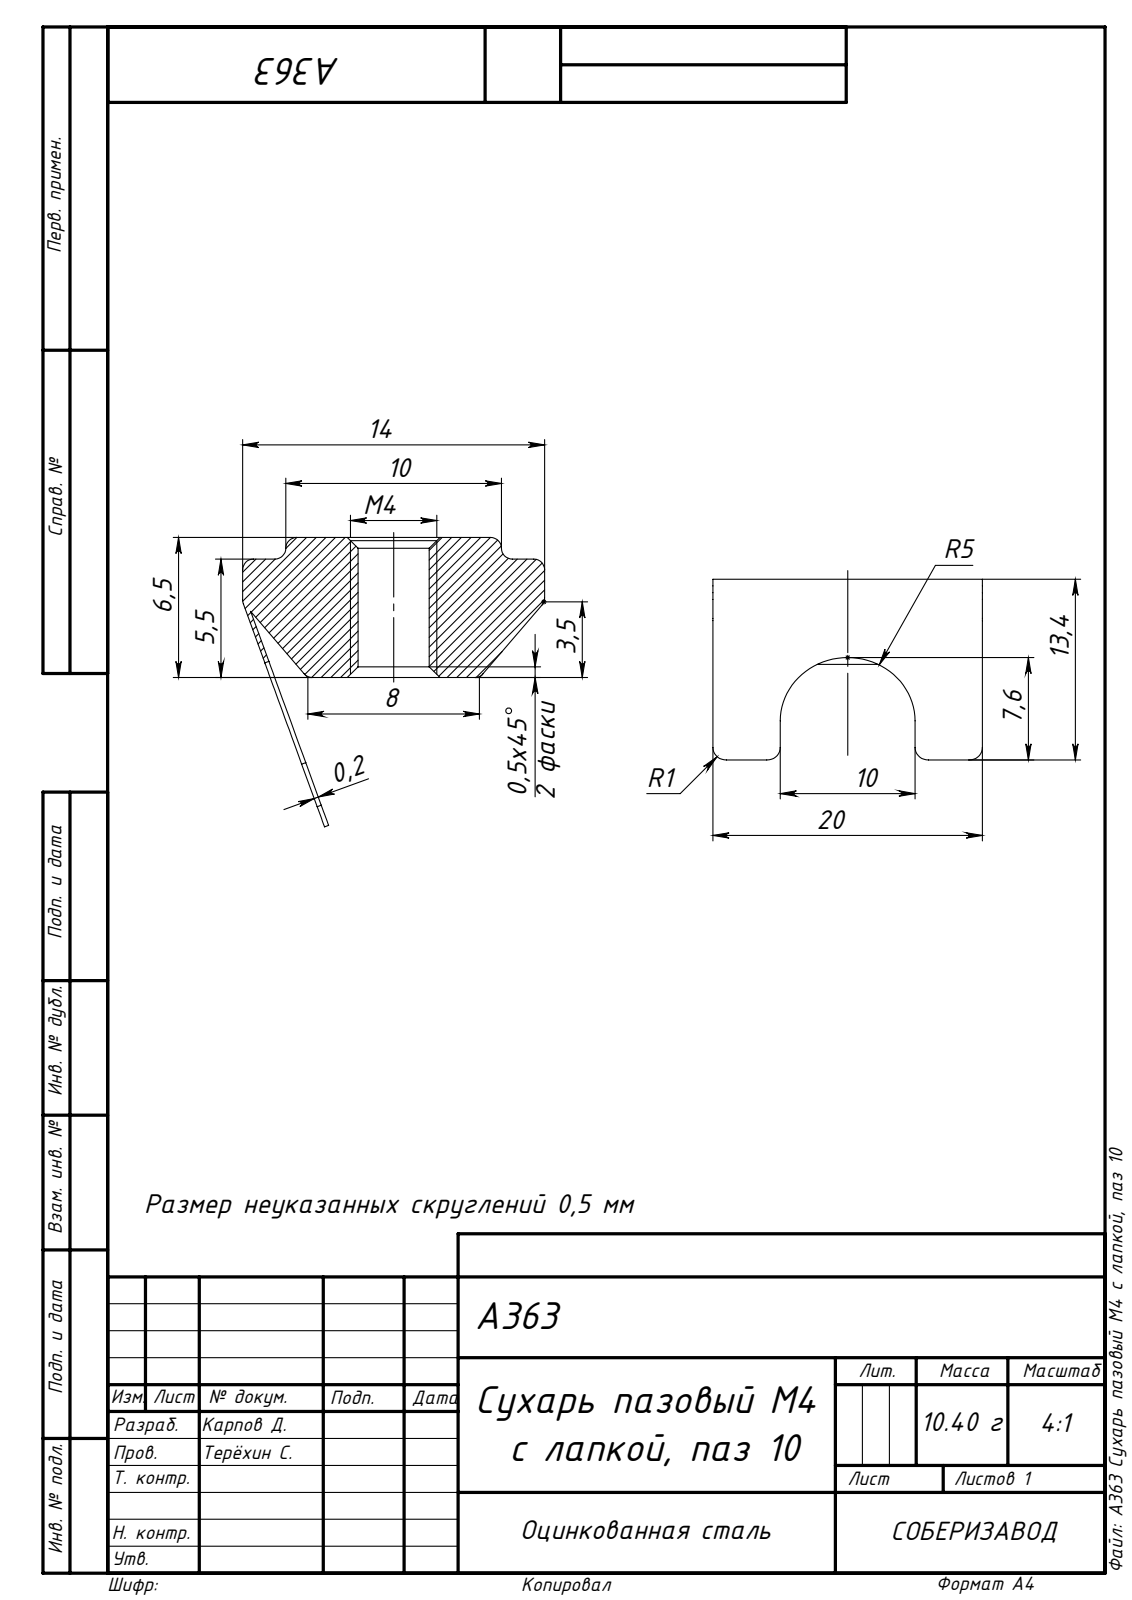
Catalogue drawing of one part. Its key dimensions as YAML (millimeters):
part_name: "A363 Сухарь пазовый М4 с лапкой, паз 10"
step_written_by: "SolidWorks 2018 (AUTOMOTIVE_DESIGN)"
units: millimeters
bodies: {solids: 1, faces: 37, planar: 16, cylindrical: 17, other: 4}
overall_size: [20, 14, 13.43]
volume: 1498
surface_area: 1205
round_holes:
  - {diameter: 3.3, count: 1}
partial_cylinders:
  - {radius: 0.5, count: 10}
  - {radius: 1, count: 4}
  - {radius: 5, count: 1}
face_to_face_distances: [6.5, 20, 1, 5.5, 14, 5, 15, 10]
